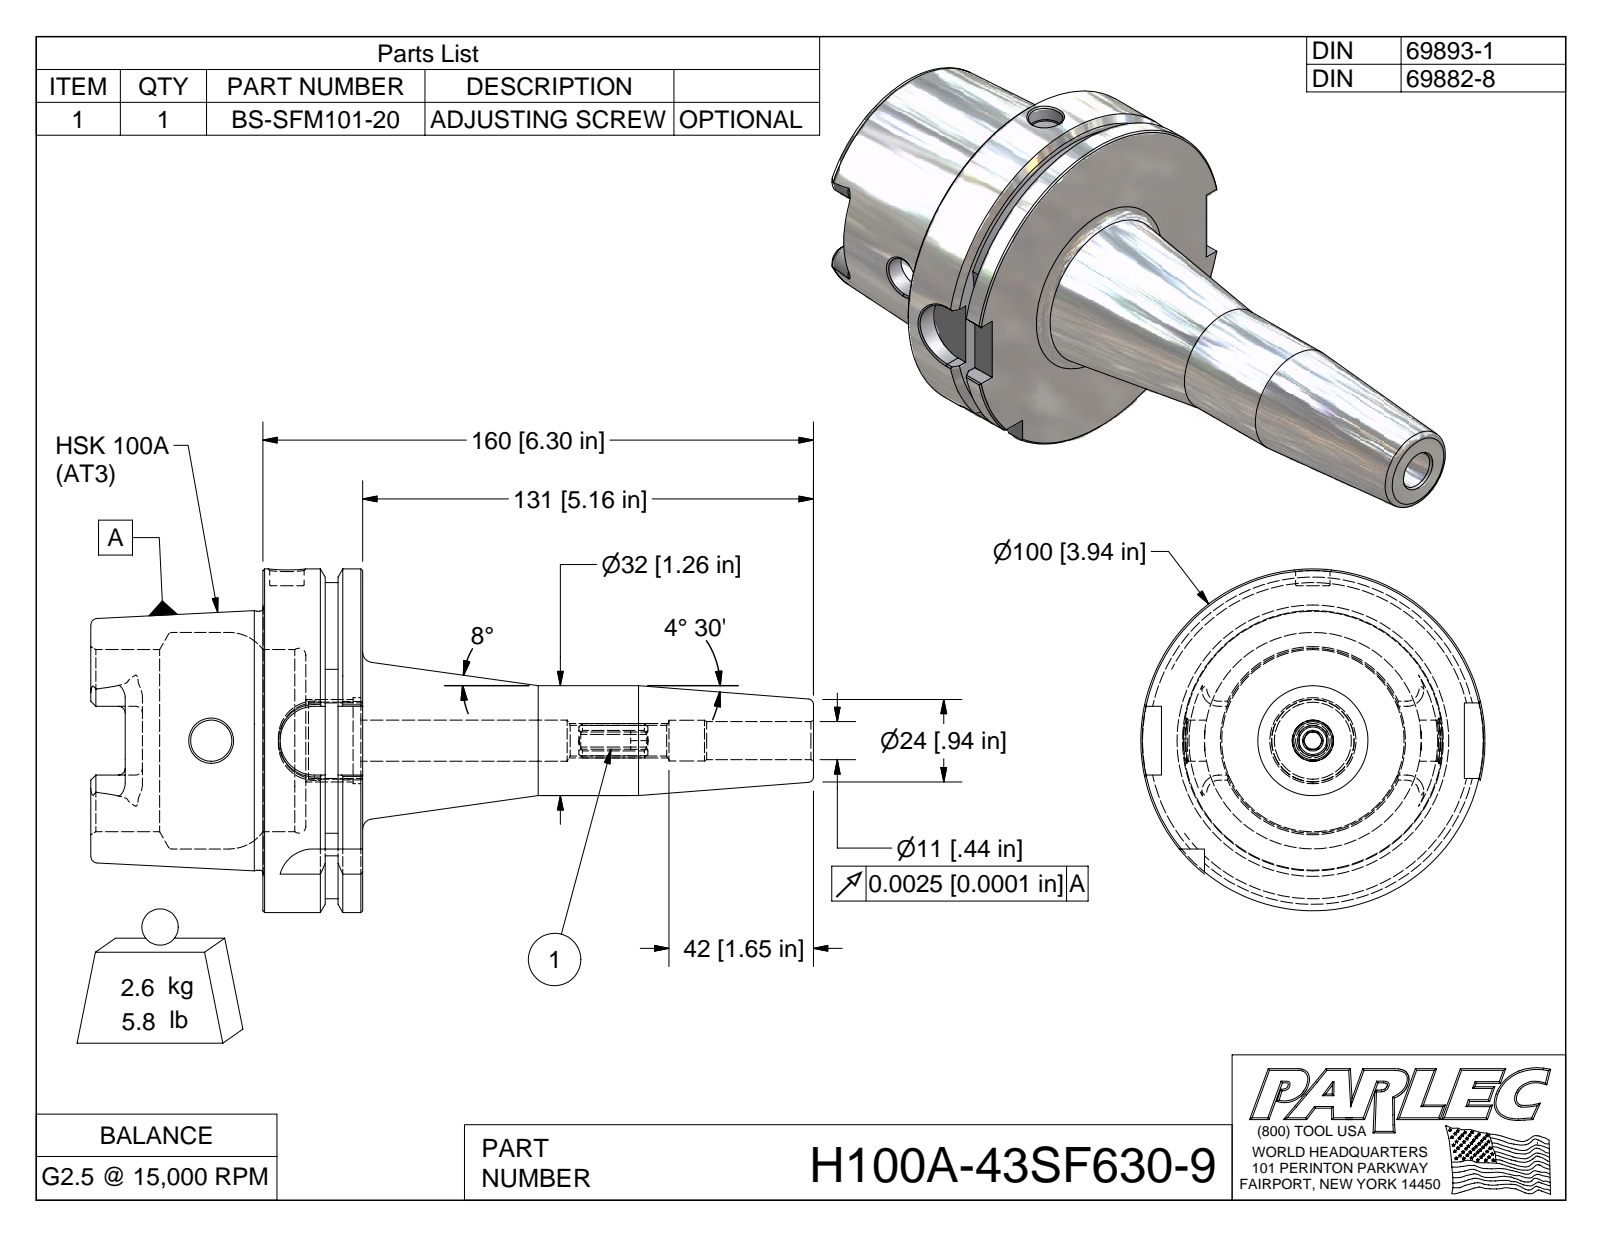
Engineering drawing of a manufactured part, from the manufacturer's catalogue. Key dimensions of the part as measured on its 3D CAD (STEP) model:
Part name (STEP PRODUCT): H100A-43SF630-9; H100A-43SF630-9-1; BS-SFM101-20
STEP written by: Autodesk Inventor 2009 (AUTOMOTIVE_DESIGN)
Units: inches
Bodies: 2 solids, 150 faces (49 planar, 30 cylindrical, 71 other)
Overall size (bounding box): 8.269 × 3.937 × 3.937
Volume: 21.92 in³ · Surface area: 105.2 in²
Round holes (diameter × count): ⌀0.394 ×1, ⌀0.437 ×1, ⌀0.467 ×1, ⌀0.472 ×1, ⌀0.881 ×1, ⌀0.985 ×1, ⌀2.087 ×1, ⌀2.48 ×1
Round bosses / shafts (diameter × count): ⌀3.937 ×1, ⌀2.967 ×1, ⌀1.26 ×1
Partial cylindrical surfaces — rounded edges, fillets, slot ends (radius × count): R0.394 ×4, R0.079 ×3, R0.192 ×2, R0.197 ×1, R1.811 ×1
Main face-to-face distances: 1.142, 0.492, 0.65, 1.969, 2.461, 3.11, 2.682, 0.713, 0.221, 0.428
